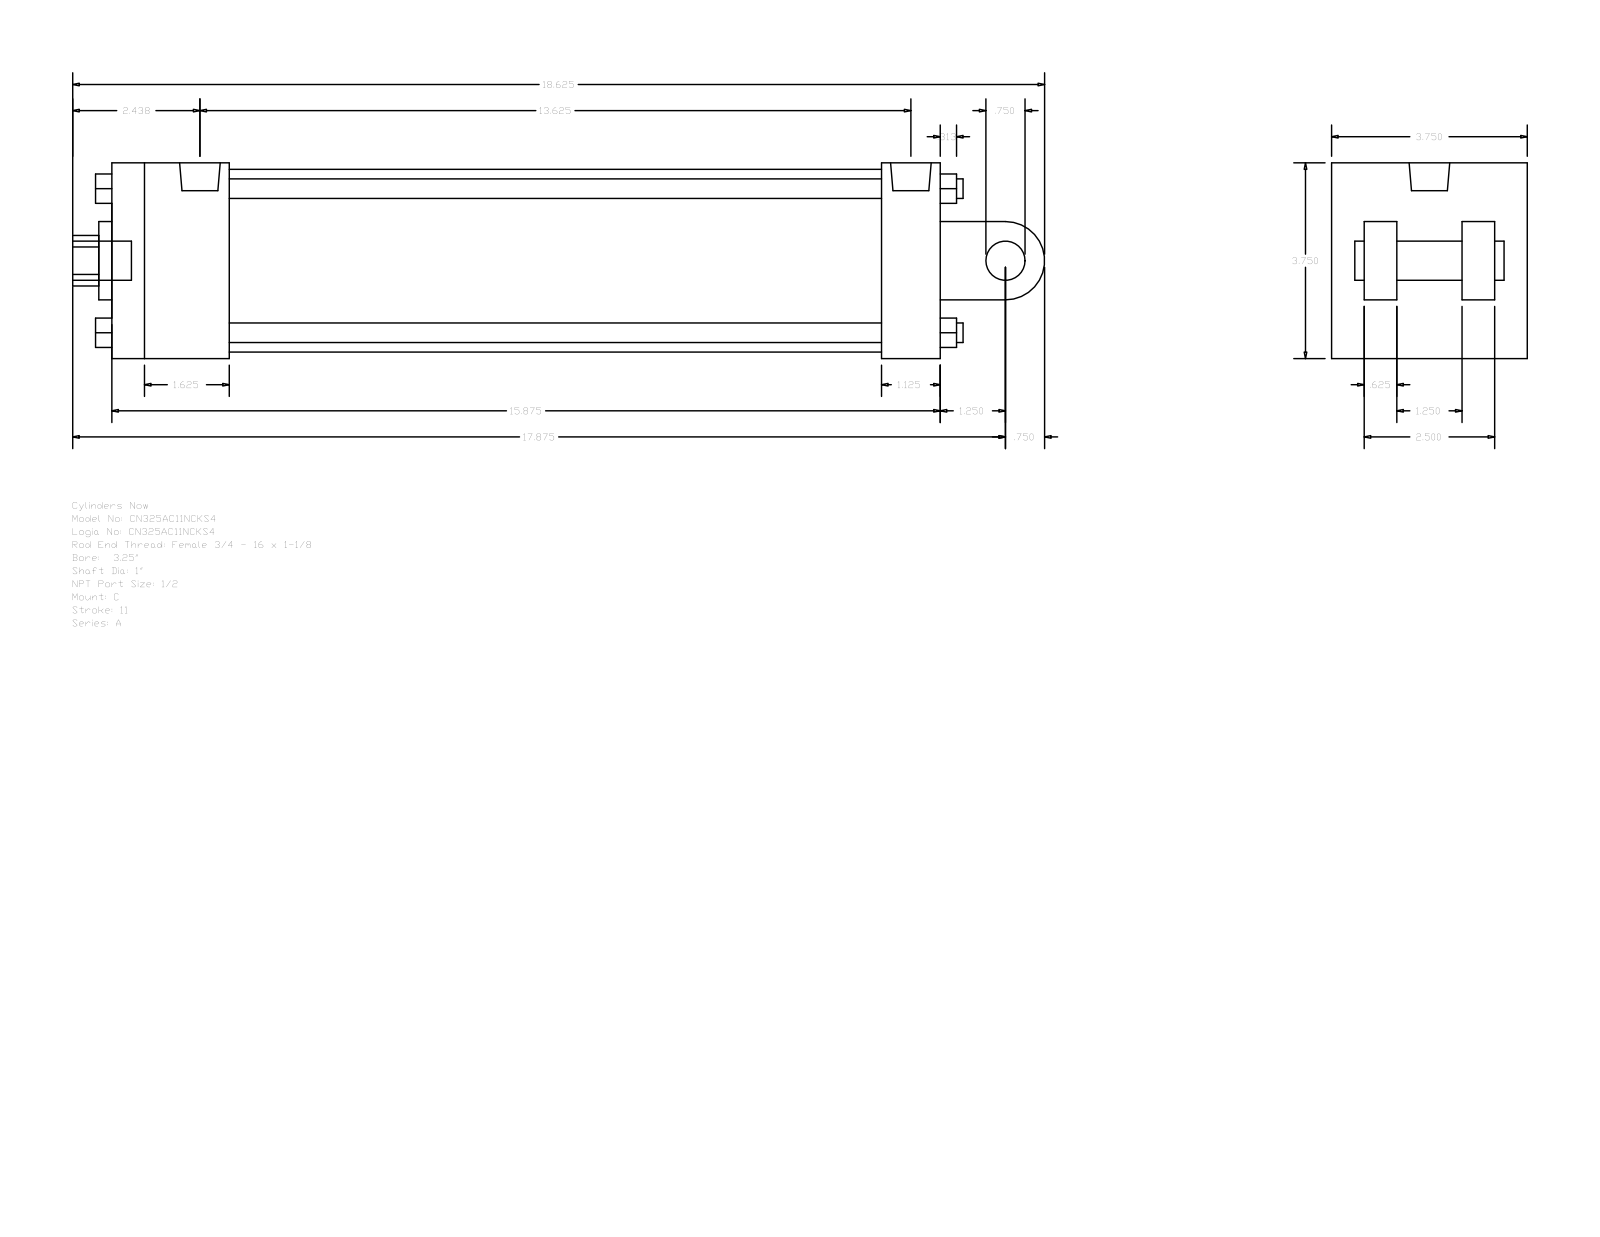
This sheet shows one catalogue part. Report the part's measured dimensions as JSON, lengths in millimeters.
{"part_name": "A_C__0325_1", "step_written_by": "GSSL Pune (CONFIG_CONTROL_DESIGN)", "units": "millimeters", "bodies": {"solids": 0, "faces": 135, "planar": 102, "cylindrical": 33, "other": 0}, "overall_size": [473.07, 95.25, 95.25], "round_holes": [[8.73, 2], [19.77, 1], [25.4, 1], [38.1, 1], [88.9, 1]], "round_bosses_or_shafts": [[9.53, 4], [19.05, 2], [8.73, 2], [19.77, 1]], "partial_cylinders_radius": [[12.29, 1], [19.05, 1]], "face_to_face_distances": [95.24, 403.22, 15.87, 63.5, 28.57, 47.63, 79.37, 31.74, 66.67, 374.65], "hole_center_spacings": [3.18]}
